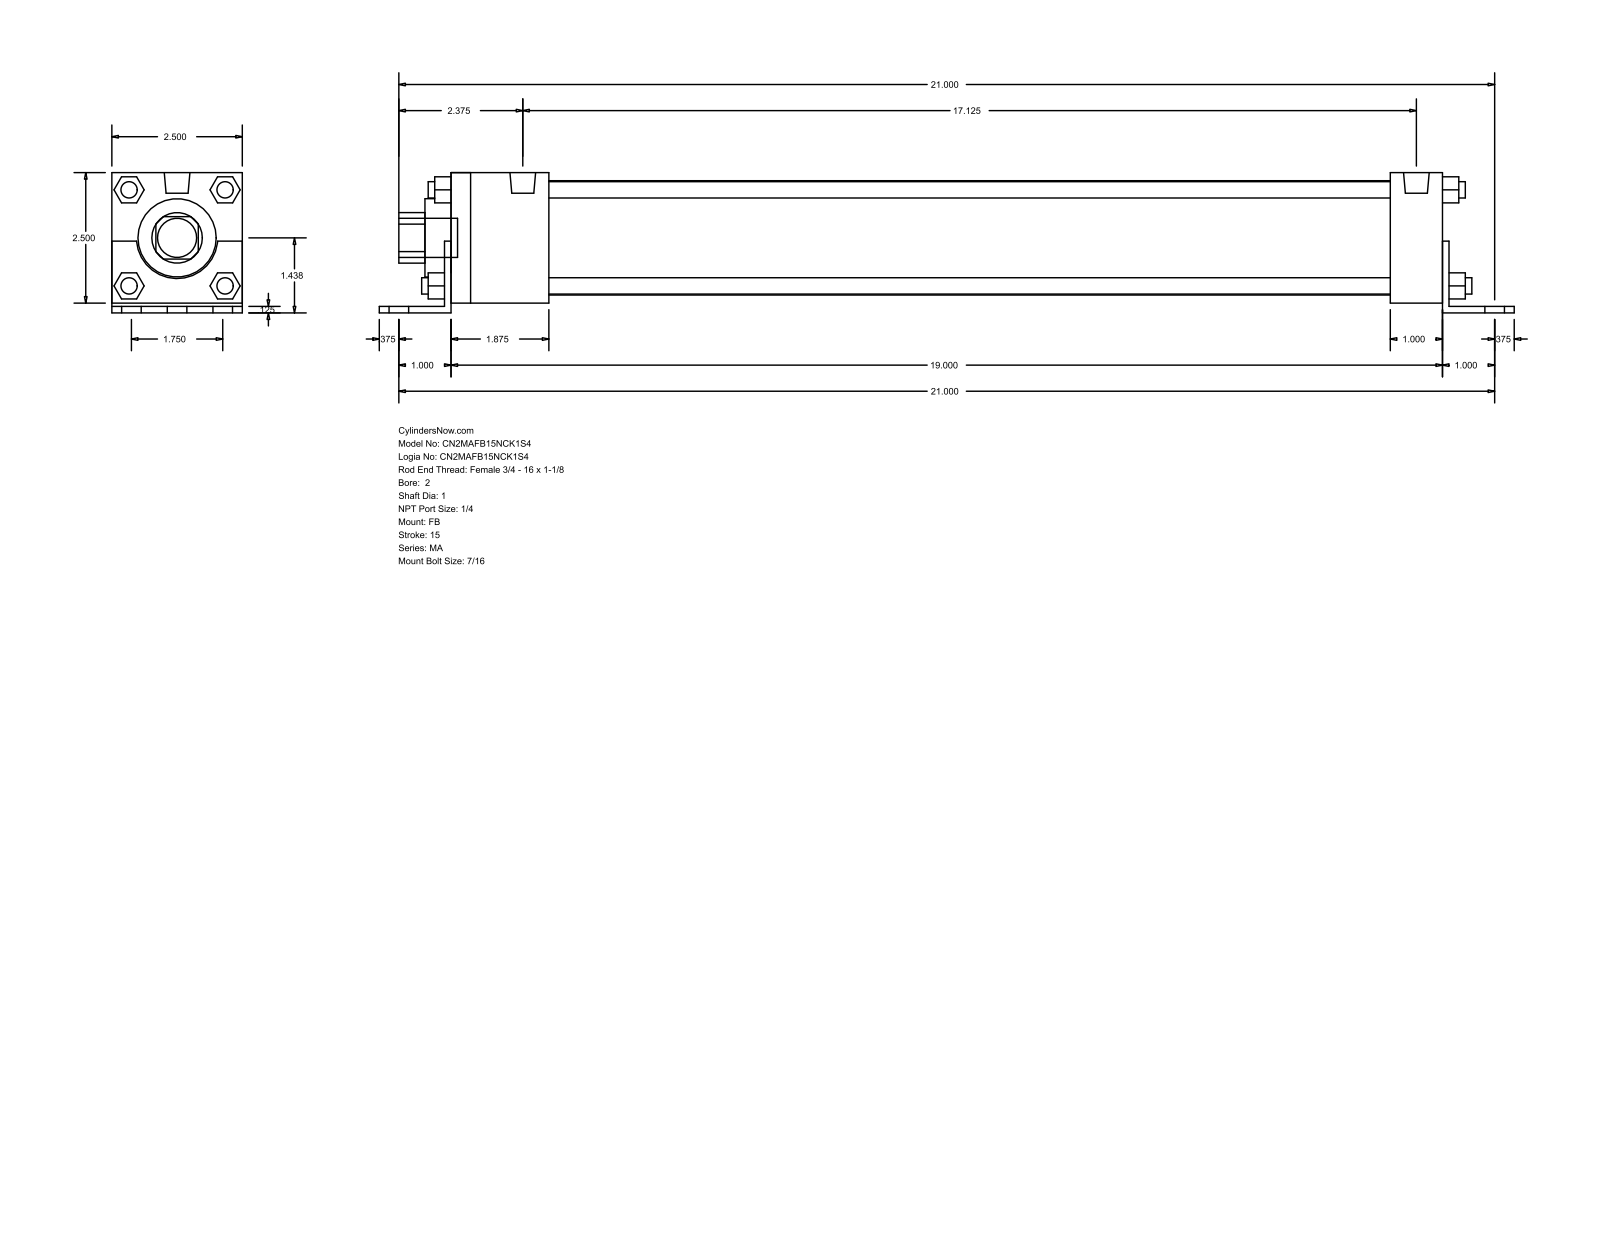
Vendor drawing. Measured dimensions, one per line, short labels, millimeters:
name: MA_FB__0200_1
written by: GSSL Pune (CONFIG_CONTROL_DESIGN)
unit: mm
bodies: 0 solids, 140 faces (105 planar, 35 cylindrical, 0 other)
size: 552.45 × 68.26 × 63.5
holes: 1× ⌀25.4, 1× ⌀38.1, 1× ⌀55.63
bosses: 8× ⌀7.94, 6× ⌀11.11, 2× ⌀12.49, 1× ⌀19.05
rounds: 1× R12.29, 1× R19.81
face distances: 63.5, 3.17, 4.76, 68.26, 1.59, 65.09, 12.7, 3.18, 482.6, 485.78
